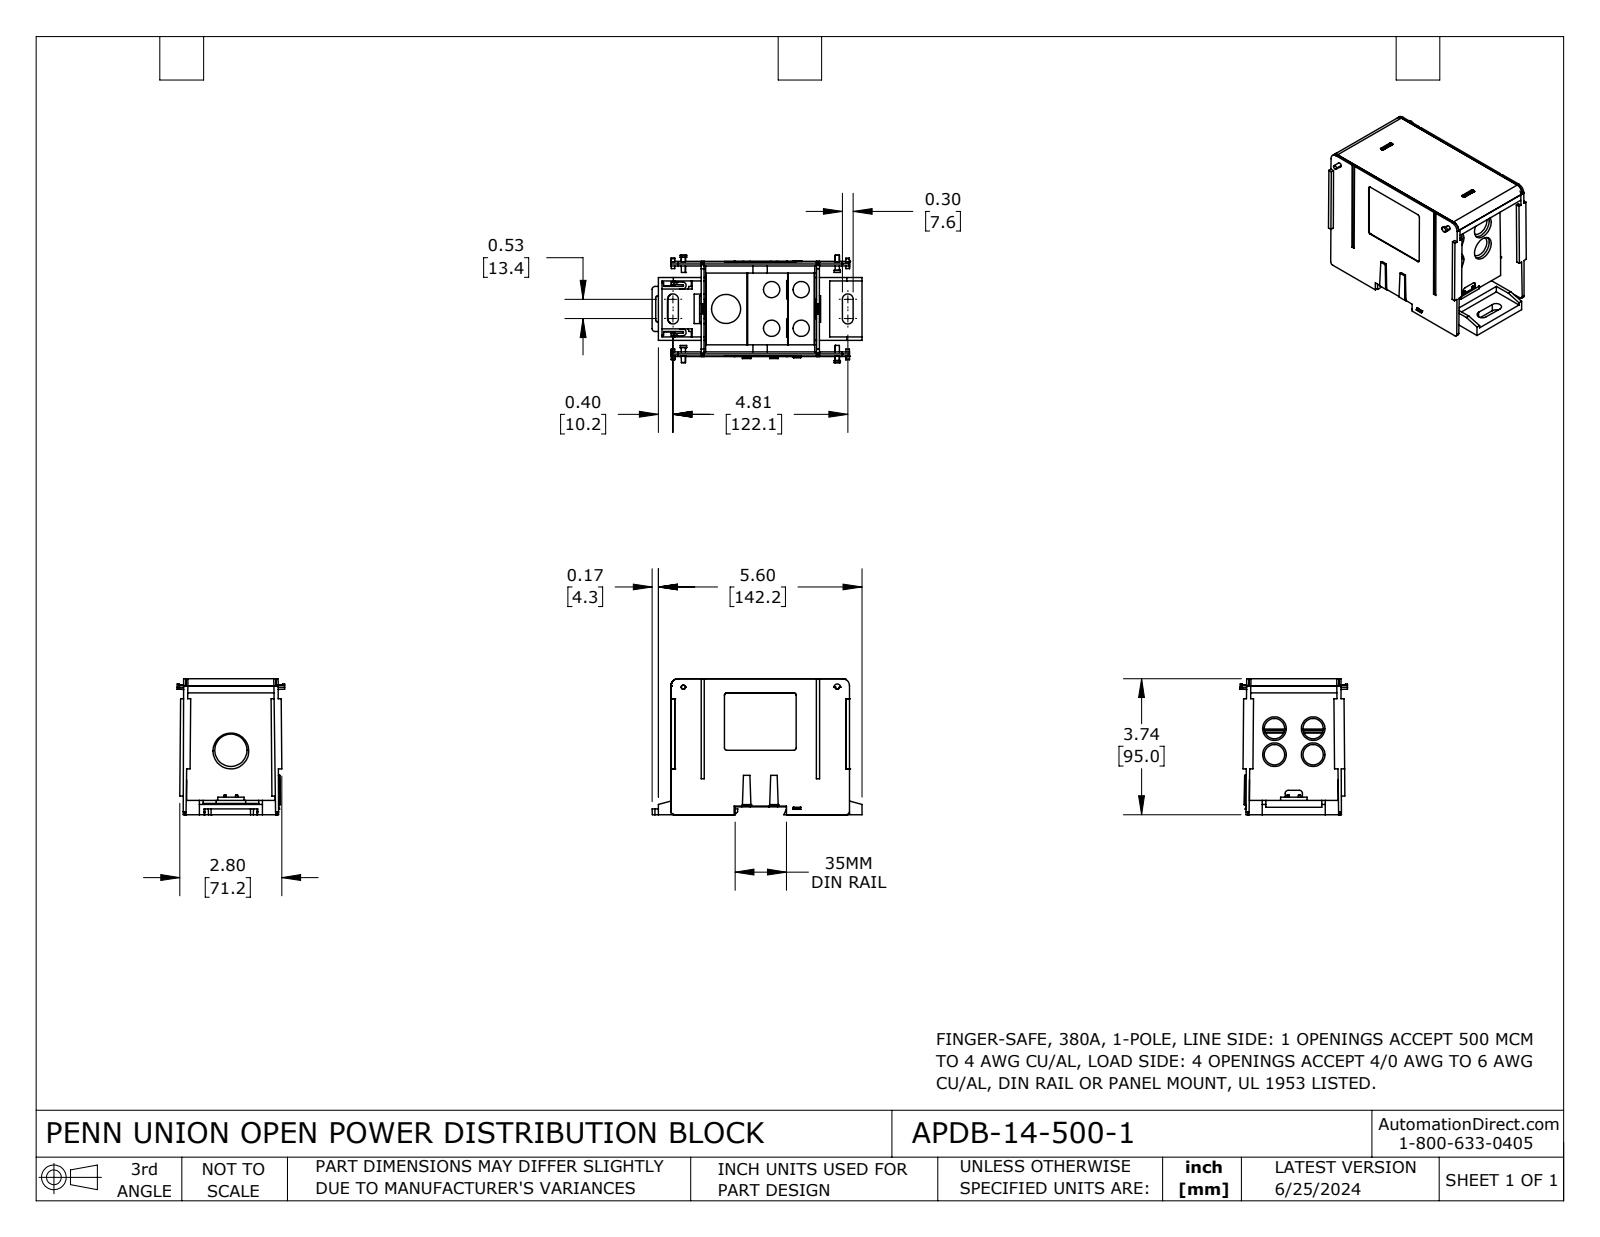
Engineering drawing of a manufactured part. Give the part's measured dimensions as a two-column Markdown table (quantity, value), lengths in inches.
| quantity | value |
| --- | --- |
| part name | APDB-14-500-1 |
| STEP written by | SolidWorks 2023 (CONFIG_CONTROL_DESIGN) |
| units | inches |
| bodies | 10 solids, 792 faces (557 planar, 164 cylindrical, 71 other) |
| overall size | 5.77 × 3.741 × 2.955 |
| volume | 20.8 in³ |
| surface area | 239.1 in² |
| round holes (diameter × count) | 0.446 × 4, 0.559 × 4, 0.65 × 4, 0.213 × 1, 0.798 × 1, 0.886 × 1, 0.984 × 1 |
| partial cylindrical surfaces (radius × count) | 0.02 × 32, 0.059 × 18, 0.039 × 10, 0.079 × 10, 0.197 × 10, 0.012 × 6, 0.089 × 4, 0.15 × 4 |
| main face-to-face distances | 0.079, 3.169, 2.54, 0.071, 2.469, 0.02, 1.043, 3.091, 3.248, 1.201 |
| hole center spacings | 1.063, 0.541, 0.545, 0.618, 0.717, 0.797, 0.812, 0.813 |
